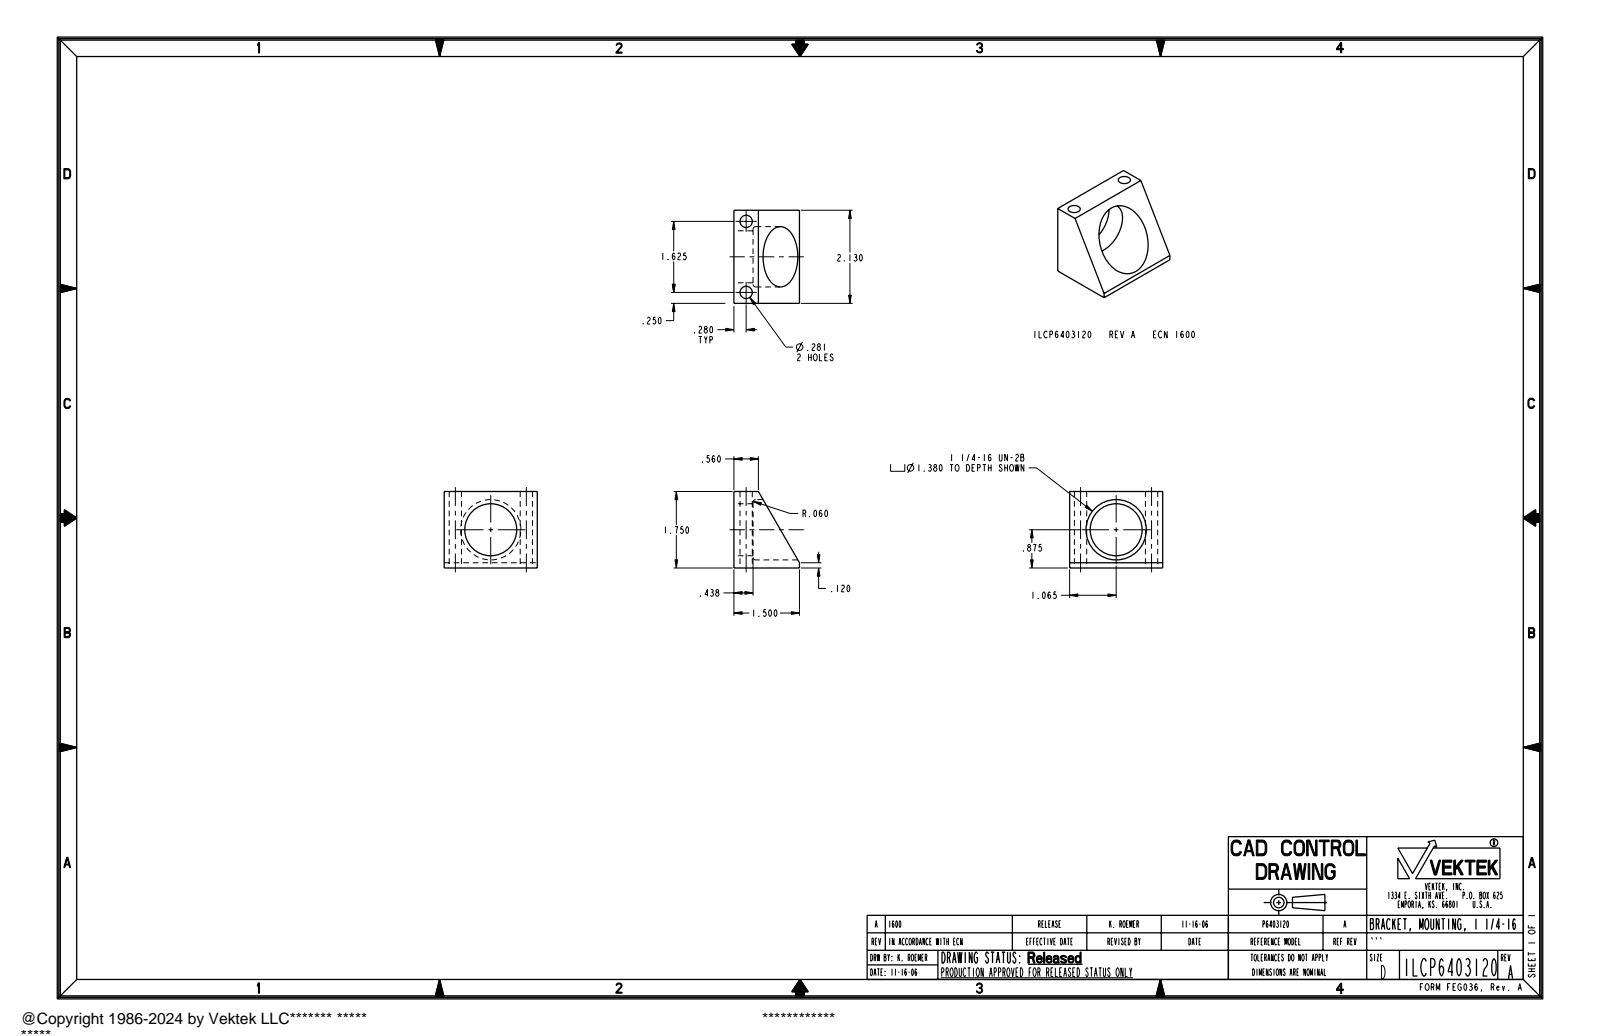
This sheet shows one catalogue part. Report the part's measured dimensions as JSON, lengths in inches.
{"part_name": "ILCP6403120", "step_written_by": "PRO/ENGINEER BY PARAMETRIC TECHNOLOGY CORPORATION, 2005180 (AUTOMOTIVE_DESIGN_CC2)", "units": "inches", "bodies": {"solids": 1, "faces": 18, "planar": 8, "cylindrical": 8, "other": 2}, "overall_size": [2.13, 1.75, 1.5], "volume_in3": 2.322, "surface_area_in2": 20.73, "round_holes": [[0.281, 2], [1.189, 1], [1.38, 1]], "face_to_face_distances": [2.13, 1.75, 1.5, 1.062, 0.438], "hole_center_spacings": [1.625]}
